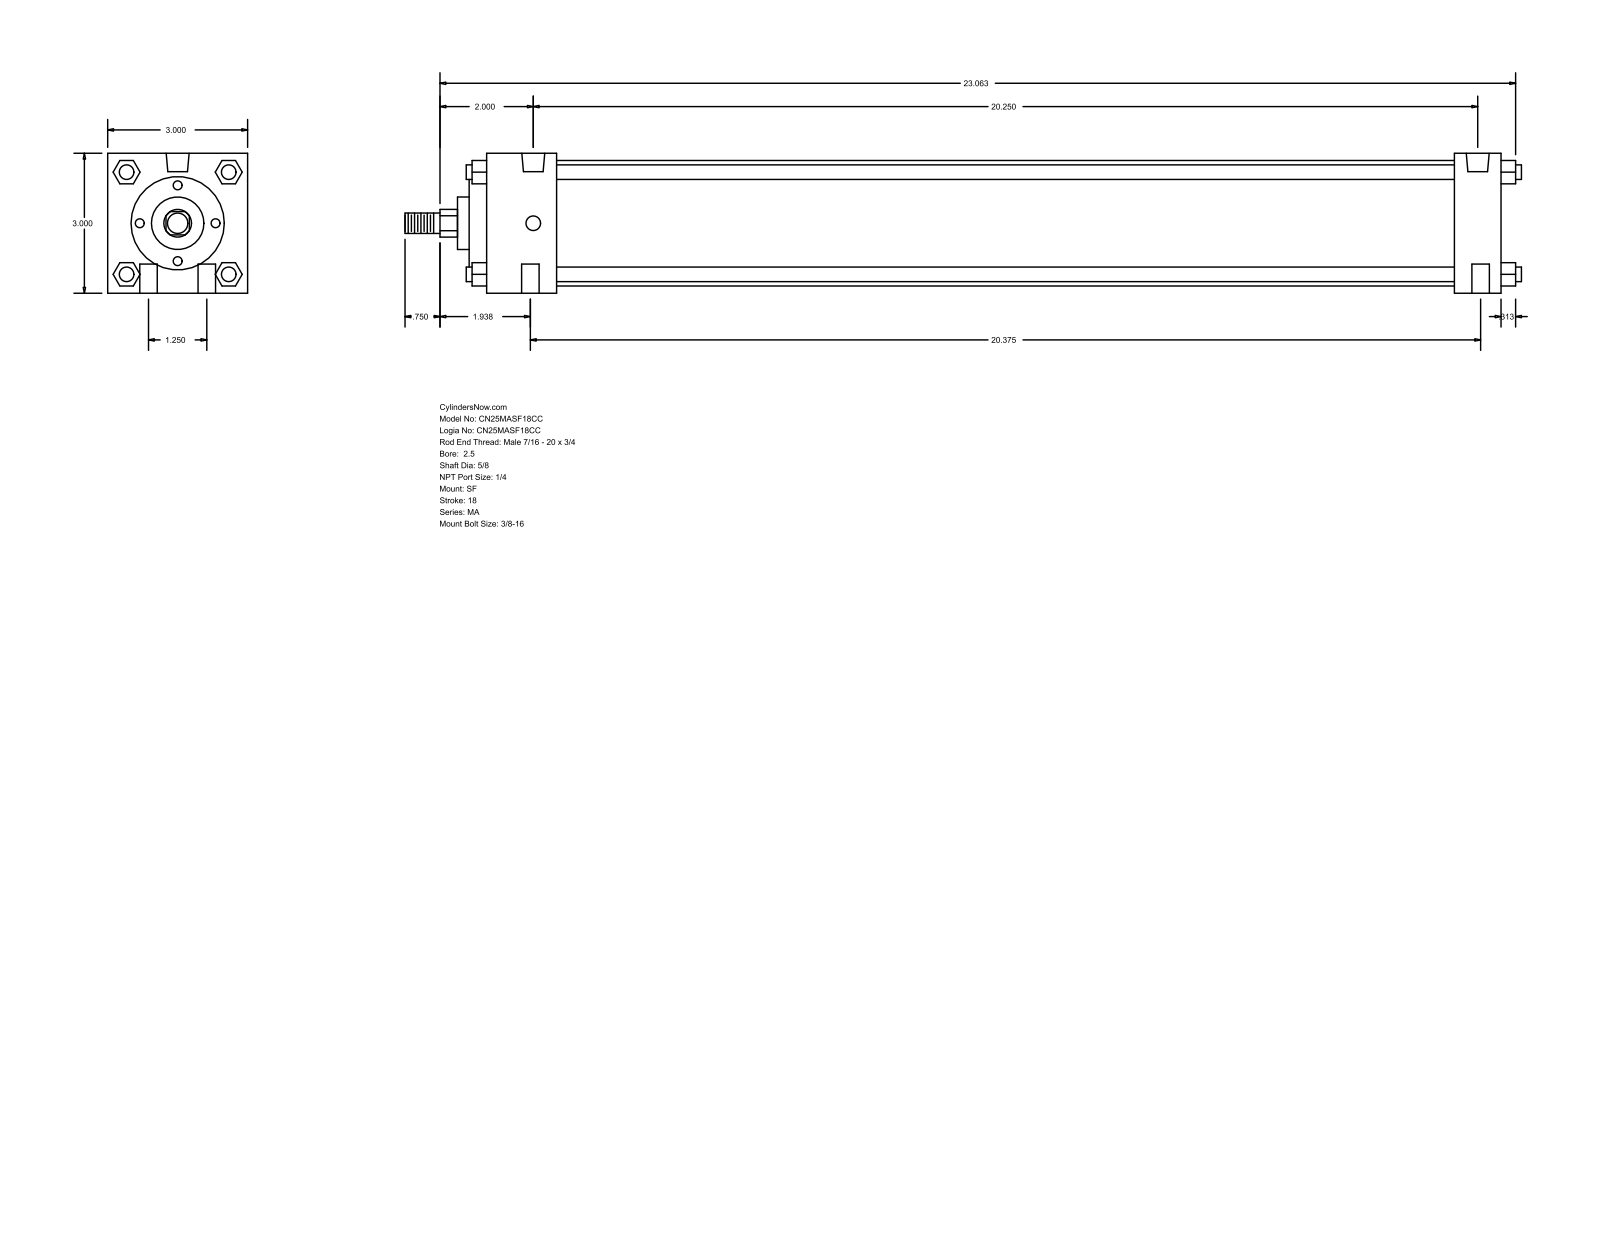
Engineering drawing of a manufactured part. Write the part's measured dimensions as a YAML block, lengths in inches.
part_name: "MA_SF__0250_0.625"
step_written_by: "GSSL Pune (CONFIG_CONTROL_DESIGN)"
units: inches
bodies: {solids: 0, faces: 126, planar: 95, cylindrical: 31, other: 0}
overall_size: [23.937, 3, 3]
round_holes:
  - {diameter: 0.375, count: 4}
  - {diameter: 0.313, count: 2}
  - {diameter: 0.492, count: 2}
round_bosses_or_shafts:
  - {diameter: 0.313, count: 4}
  - {diameter: 2.69, count: 1}
  - {diameter: 2, count: 1}
  - {diameter: 1.125, count: 1}
  - {diameter: 0.625, count: 1}
  - {diameter: 0.437, count: 1}
partial_cylinders:
  - {radius: 0.297, count: 1}
face_to_face_distances: [3, 21.75, 1, 20.75, 1.5, 19.25, 20.25, 0.5, 0.375, 1.875]
hole_center_spacings: [0.628, 20.322, 1.25, 20.25, 20.375, 20.413]
